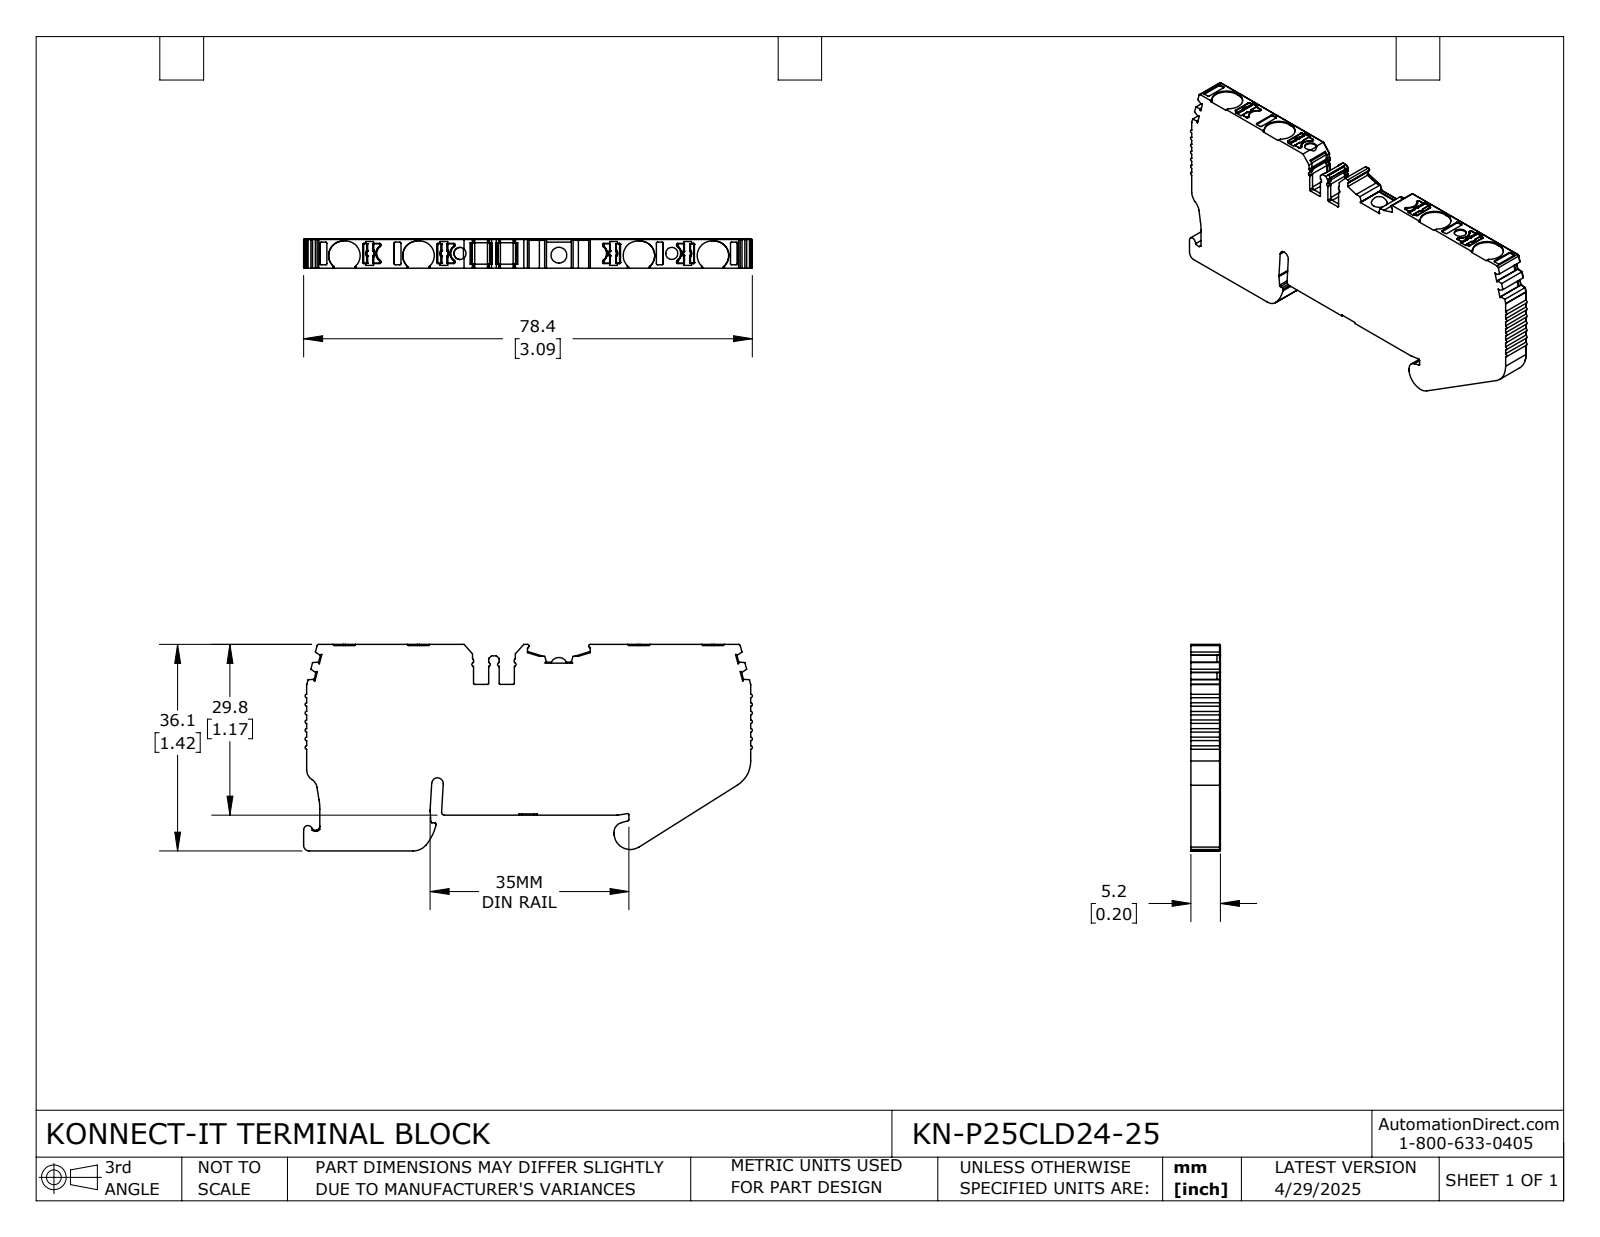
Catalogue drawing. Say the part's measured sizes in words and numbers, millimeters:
The part is named "KN-P25CLD24-25". Its 3-D file was written by "SolidWorks 2024 (CONFIG_CONTROL_DESIGN)". It is 1 solid with 740 faces: 381 planar, 291 cylindrical and 68 other. Overall it measures 78.36 by 36.07 by 5.15 millimeters. Its volume is 11 975 cubic millimeters and its surface area 6 221 square millimeters. Round holes: 2 of diameter 2.1. Partial cylindrical surfaces (rounded edges, fillets, slot ends): 78 of radius 0.2, 39 of radius 0.3, 21 of radius 0.1, 18 of radius 0.5, 16 of radius 0.15, 9 of radius 0.4, 8 of radius 2.55, 4 of radius 1.5. The main face-to-face distances are 5.15, 29.61, 29.81, 6.26, 35.87, 36.07, 77.52, 1.2, 5, 4.5. The hole center spacings are 36.98.
